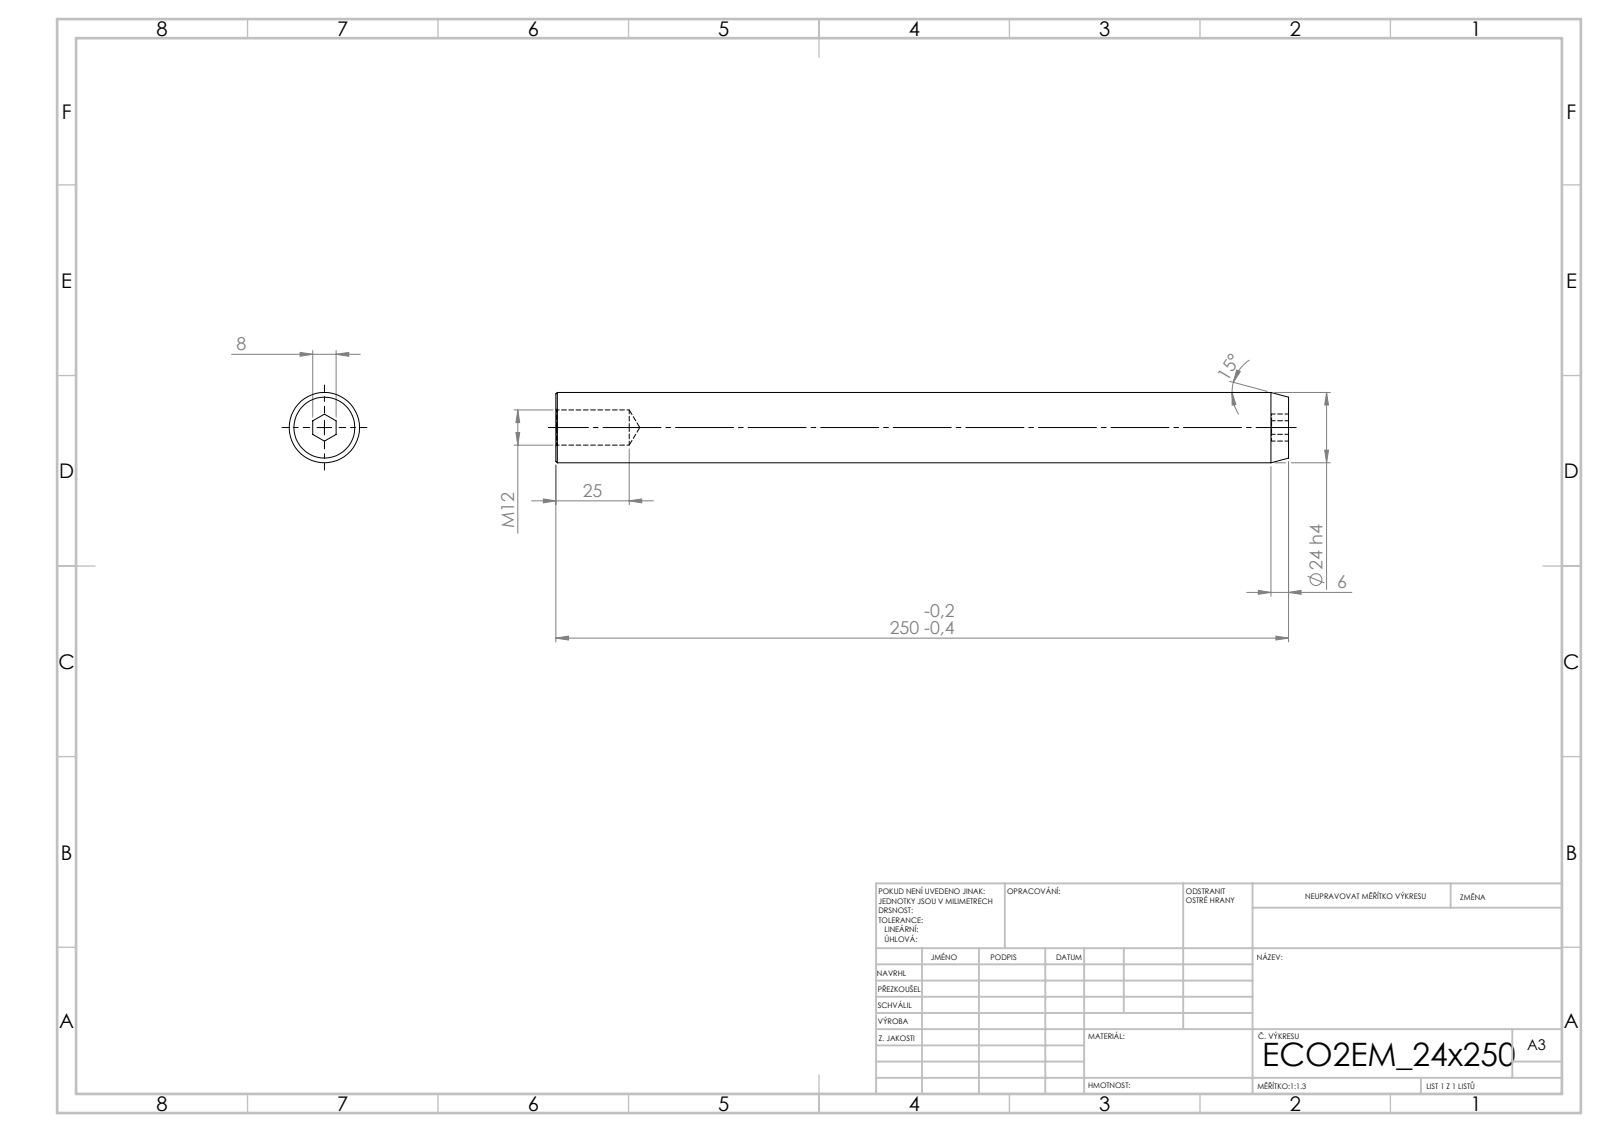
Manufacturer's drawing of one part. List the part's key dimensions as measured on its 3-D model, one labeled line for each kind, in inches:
STEP written by: SolidWorks 2019 (CONFIG_CONTROL_DESIGN)
Units: inches
Bodies: 1 solid, 21 faces (9 planar, 4 cylindrical, 8 other)
Overall size (bounding box): 9.843 × 0.945 × 0.945
Volume: 6.679 in³ · Surface area: 32.12 in²
Round holes (diameter × count): ⌀0.472 ×1
Round bosses / shafts (diameter × count): ⌀0.945 ×1
Main face-to-face distances: 9.843, 0.315, 0.228, 9.614
